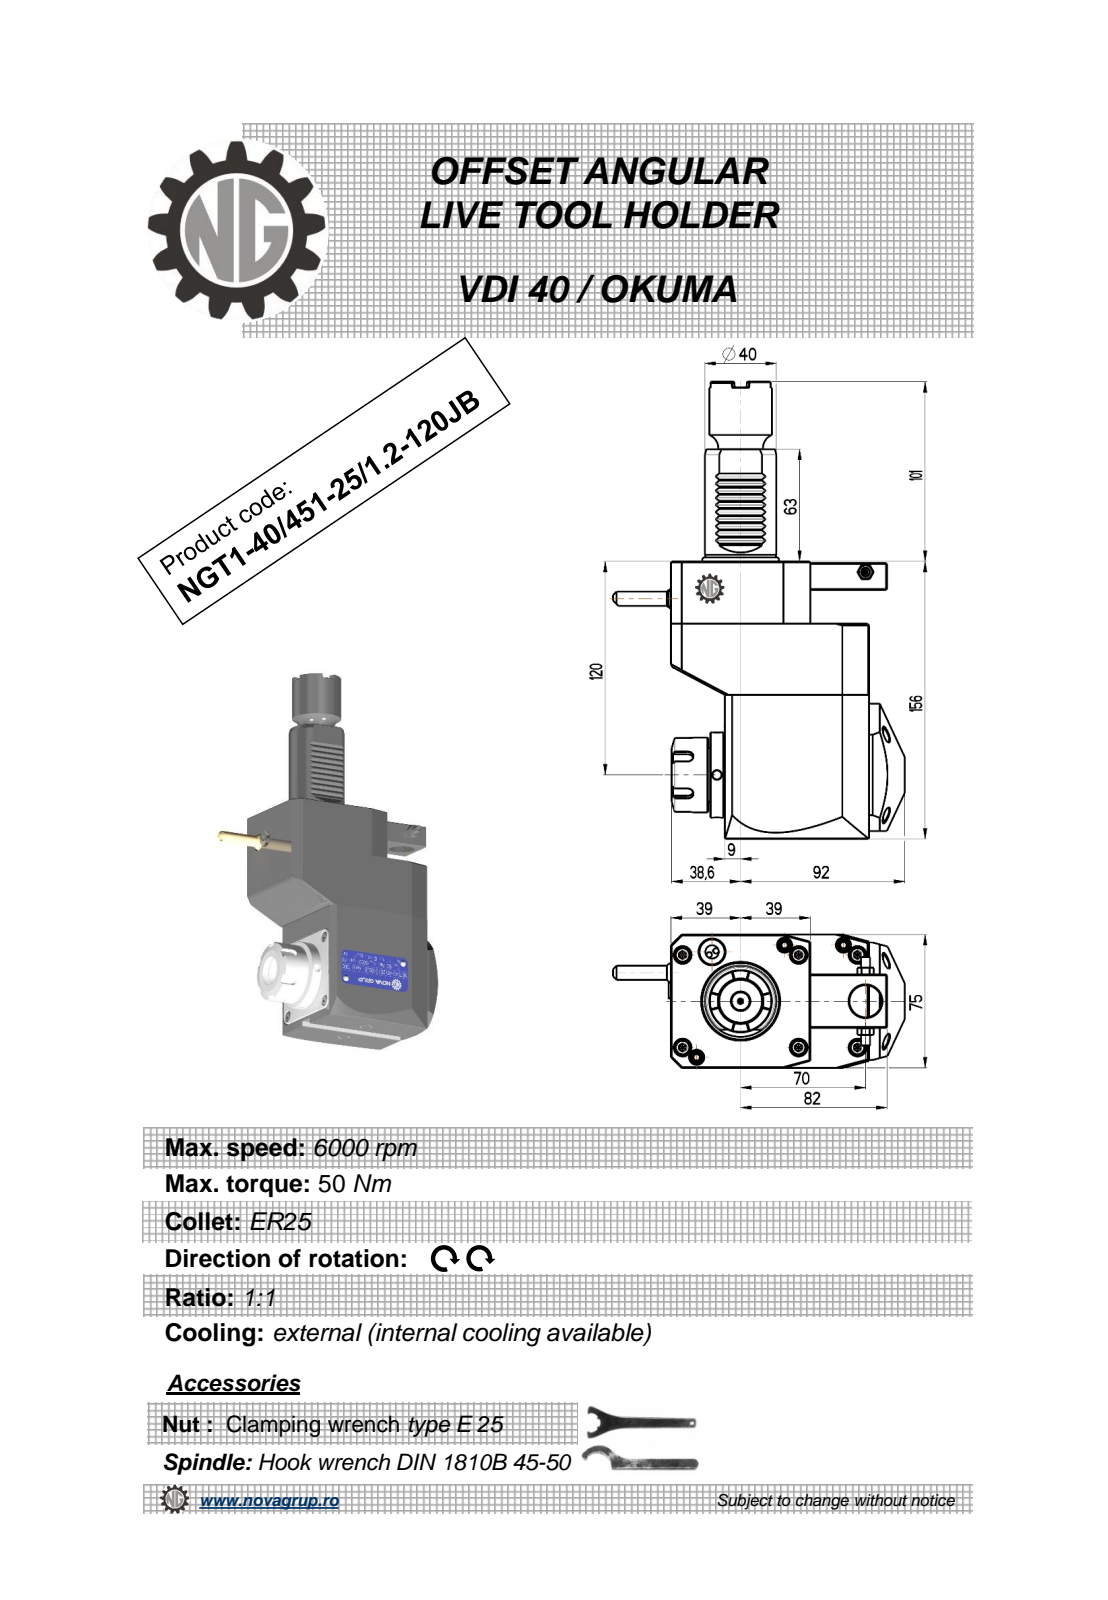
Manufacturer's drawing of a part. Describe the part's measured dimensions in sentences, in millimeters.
The part is named "NGT1_40_451_25_1_2_120JB". Its 3-D file was written by "PRO/ENGINEER BY PARAMETRIC TECHNOLOGY CORPORATION, 2010280 (CONFIG_CONTROL_DESIGN)". It is 1 solid with 500 faces: 218 planar, 95 cylindrical and 187 other. Overall it measures 257 by 163.5 by 76.6 millimeters. Its volume is 1 210 000 cubic millimeters and its surface area 93 445 square millimeters. Round holes: 3 of diameter 5, 1 of diameter 3, 1 of diameter 4.2, 1 of diameter 9.5, 1 of diameter 18, 1 of diameter 20.3, 1 of diameter 25, 1 of diameter 26.8. Round bosses or shafts: 1 of diameter 48, 1 of diameter 42, 1 of diameter 40, 1 of diameter 37.5, 1 of diameter 35, 1 of diameter 33, 1 of diameter 26.58, 1 of diameter 10. Partial cylindrical surfaces (rounded edges, fillets, slot ends): 12 of radius 0.26, 10 of radius 0.3, 6 of radius 0.2, 5 of radius 3, 1 of radius 0.5, 1 of radius 40. The main face-to-face distances are 75, 156, 111, 30, 121, 35, 81, 33, 48, 78. The hole center spacings are 13.25, 20.93, 70, 83.25, 100.28, 112.5, 141.16.
